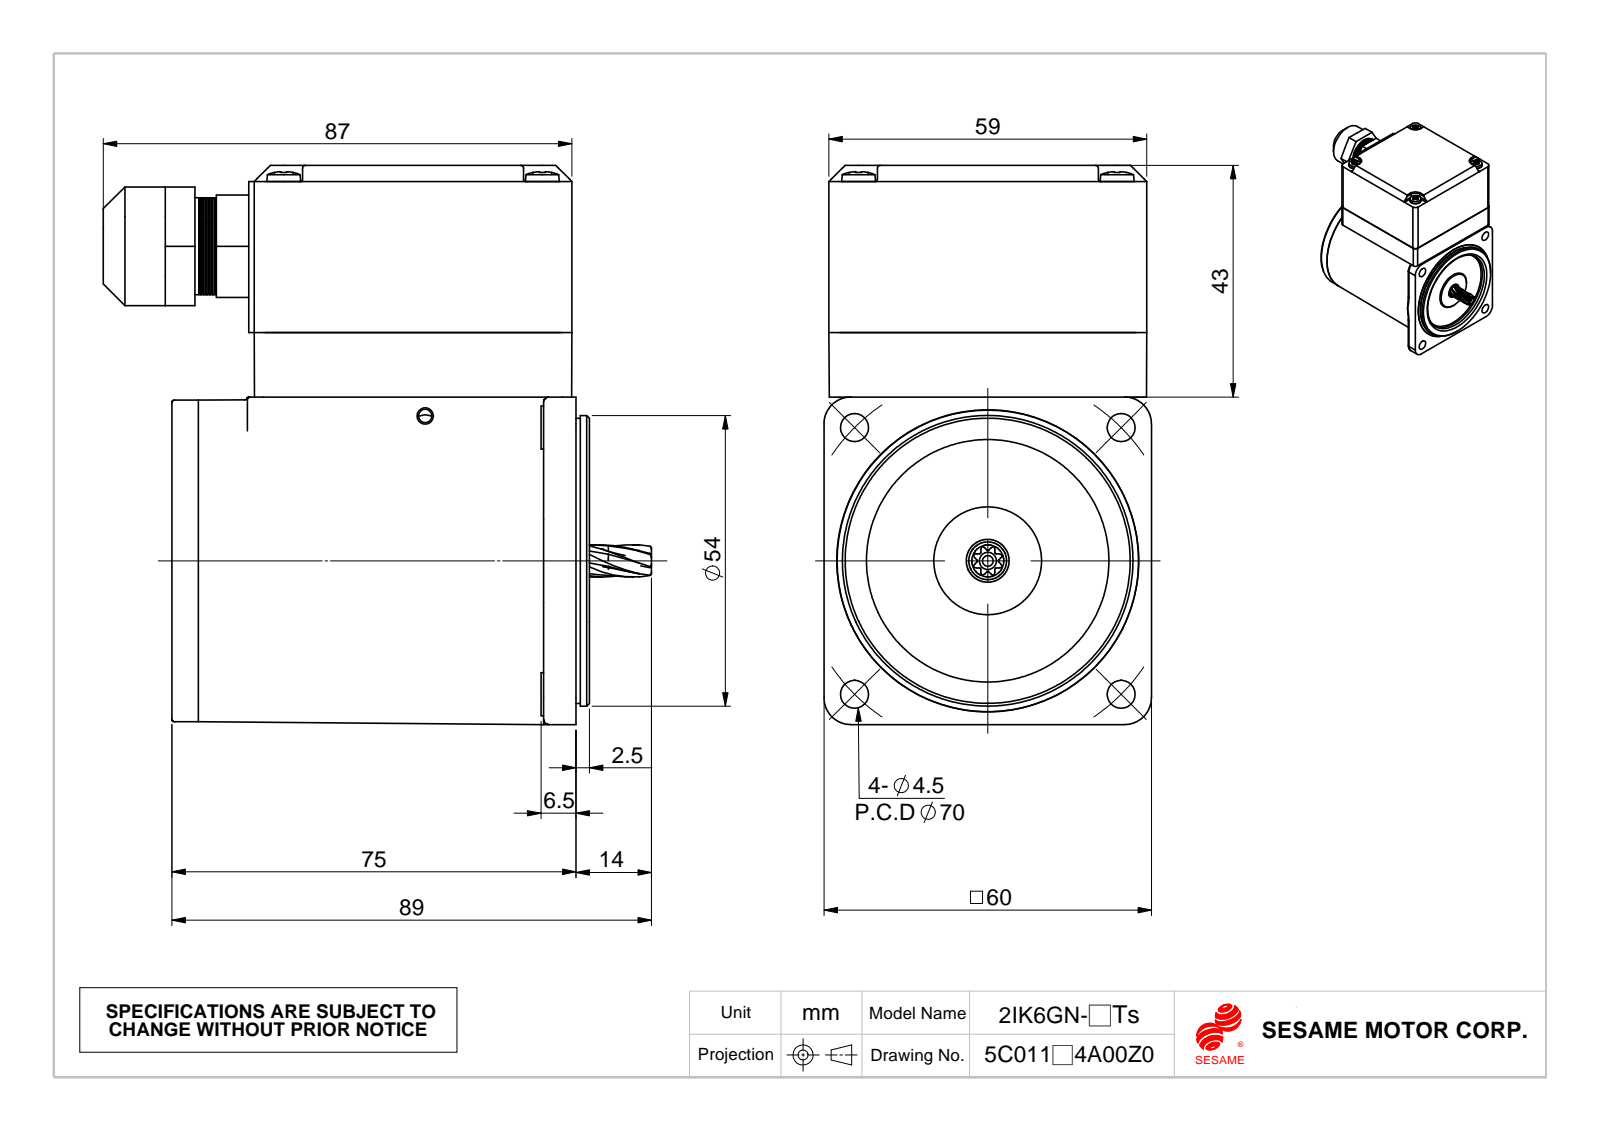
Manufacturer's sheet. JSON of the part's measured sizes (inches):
{"part_name": "成品180度; M206Ts_2.成品; C254_Default; 06GN_0成品 (+1 more)", "step_written_by": "SolidWorks 2010 (CONFIG_CONTROL_DESIGN)", "units": "inches", "bodies": {"solids": 11, "faces": 2487, "planar": 195, "cylindrical": 821, "other": 1471}, "overall_size": [4.087, 4.006, 2.394], "volume_in3": 22.99, "surface_area_in2": 98.94, "round_holes": [[0.13, 4], [0.138, 4], [0.154, 4], [0.169, 4], [0.205, 4], [0.079, 1], [0.098, 1], [0.276, 1], [0.433, 1], [0.472, 1], [0.571, 1], [1.268, 1]], "round_bosses_or_shafts": [[0.315, 4], [0.248, 4], [0.118, 4], [2.35, 1], [2.123, 1], [2.084, 1], [0.866, 1], [0.709, 1]], "partial_cylinders_radius": [[0.02, 13], [0.079, 12], [0.157, 6], [0.039, 4], [0.059, 4], [0.118, 4], [0.138, 4], [0.197, 4]], "face_to_face_distances": [0.472, 0.03, 1.22, 1.693, 0.059, 2.323, 0.039, 2.89, 2.894, 2.953], "hole_center_spacings": [1.378, 1.89, 1.949, 0.459, 0.486, 0.5, 0.981, 0.984]}
